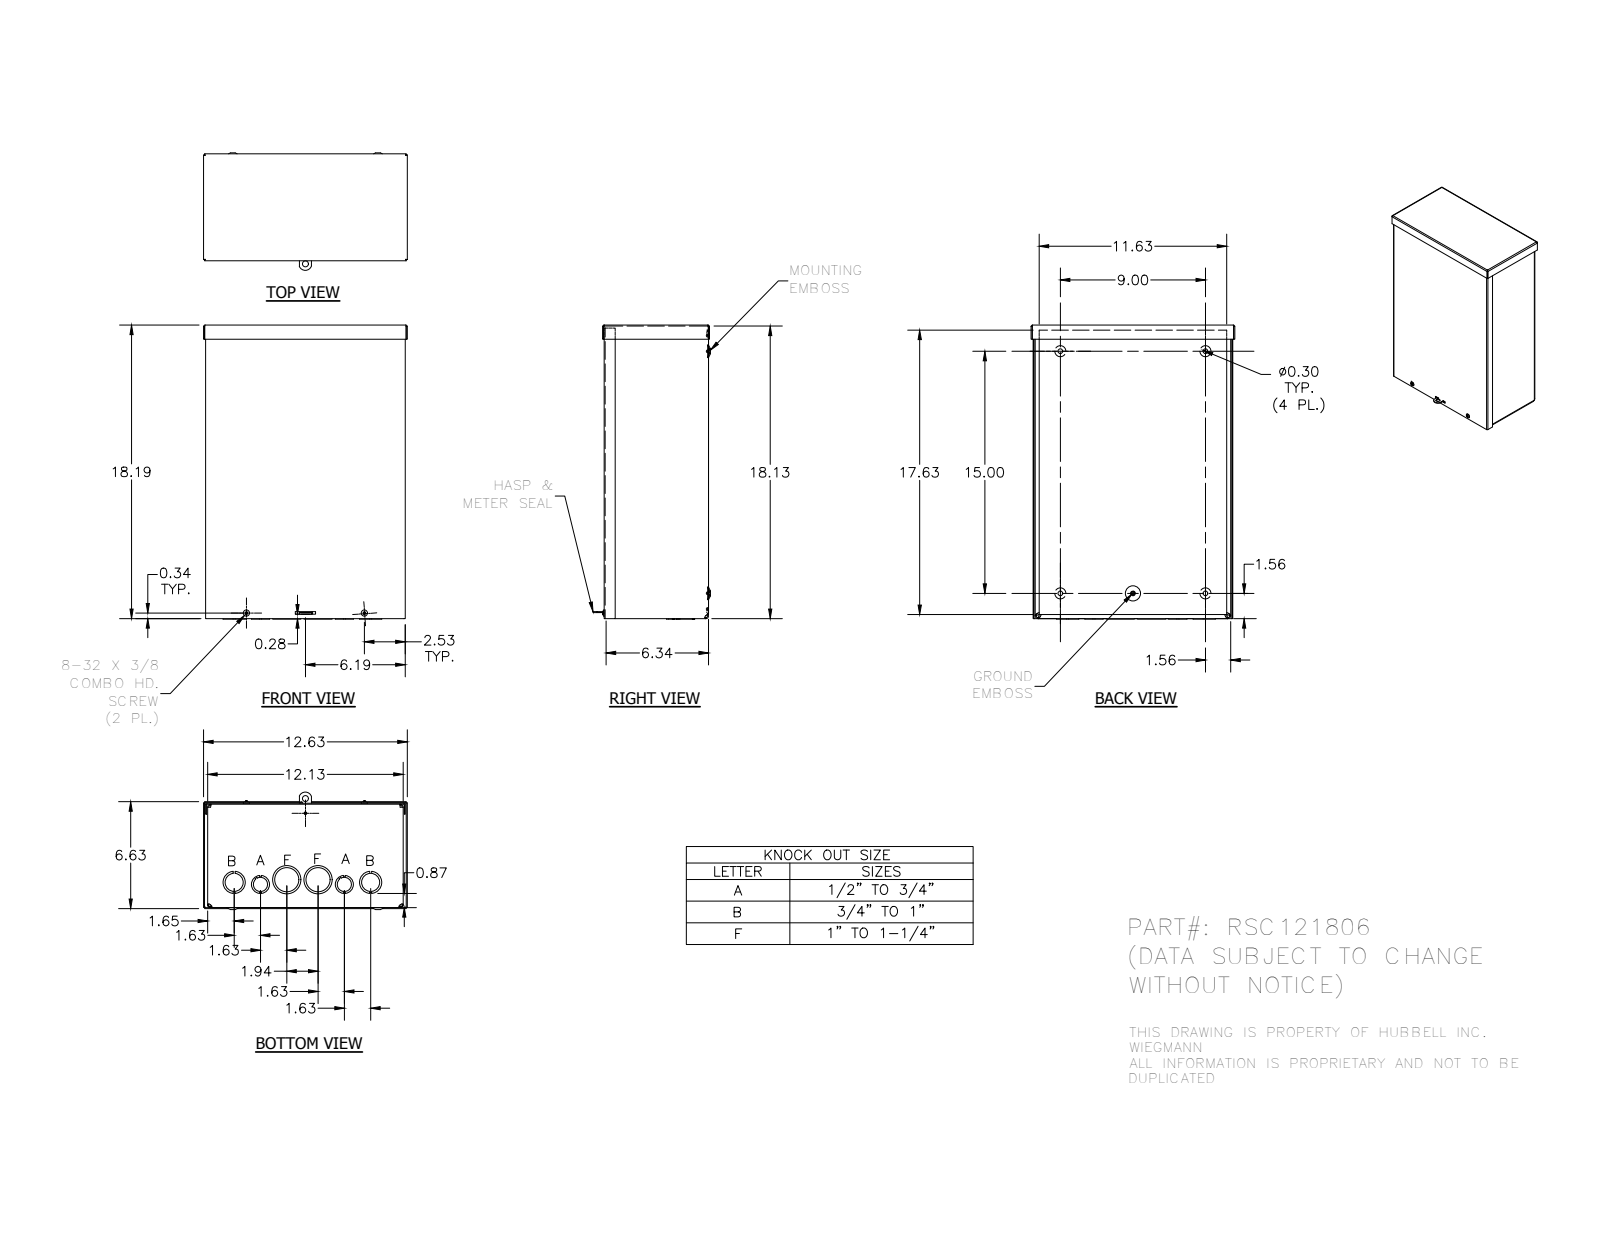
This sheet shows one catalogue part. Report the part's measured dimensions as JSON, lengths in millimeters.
{"part_name": "RSC121806; RSC121806_WRAP; RSC1218_LID; RSC1206_CAP (+4 more)", "step_written_by": "Autodesk Inventor 2012 (AUTOMOTIVE_DESIGN)", "units": "millimeters", "bodies": {"solids": 7, "faces": 551, "planar": 264, "cylindrical": 143, "other": 144}, "overall_size": [464.3, 320.7, 181], "volume_mm3": 1040000, "surface_area_mm2": 1334000, "round_holes": [[7.6, 4], [8, 4], [28.6, 4], [3.2, 2], [3.8, 2], [22.2, 2], [34.9, 2], [38.1, 2], [44.5, 2], [4, 1], [4.2, 1], [9.5, 1]], "round_bosses_or_shafts": [[9.8, 2], [4.2, 2], [5.8, 1]], "partial_cylinders_radius": [[0.3, 14], [0.8, 8], [2.4, 8], [3.2, 8], [4.7, 8], [0.8, 6], [1.4, 4], [1.6, 4]], "face_to_face_distances": [1.6, 158.7, 157.1, 1.6, 308, 1.6, 160.3, 158.8, 460.4, 3.1], "hole_center_spacings": [34.4, 41.5, 42.1, 82.9, 91, 114.3, 132.2, 173.5]}
